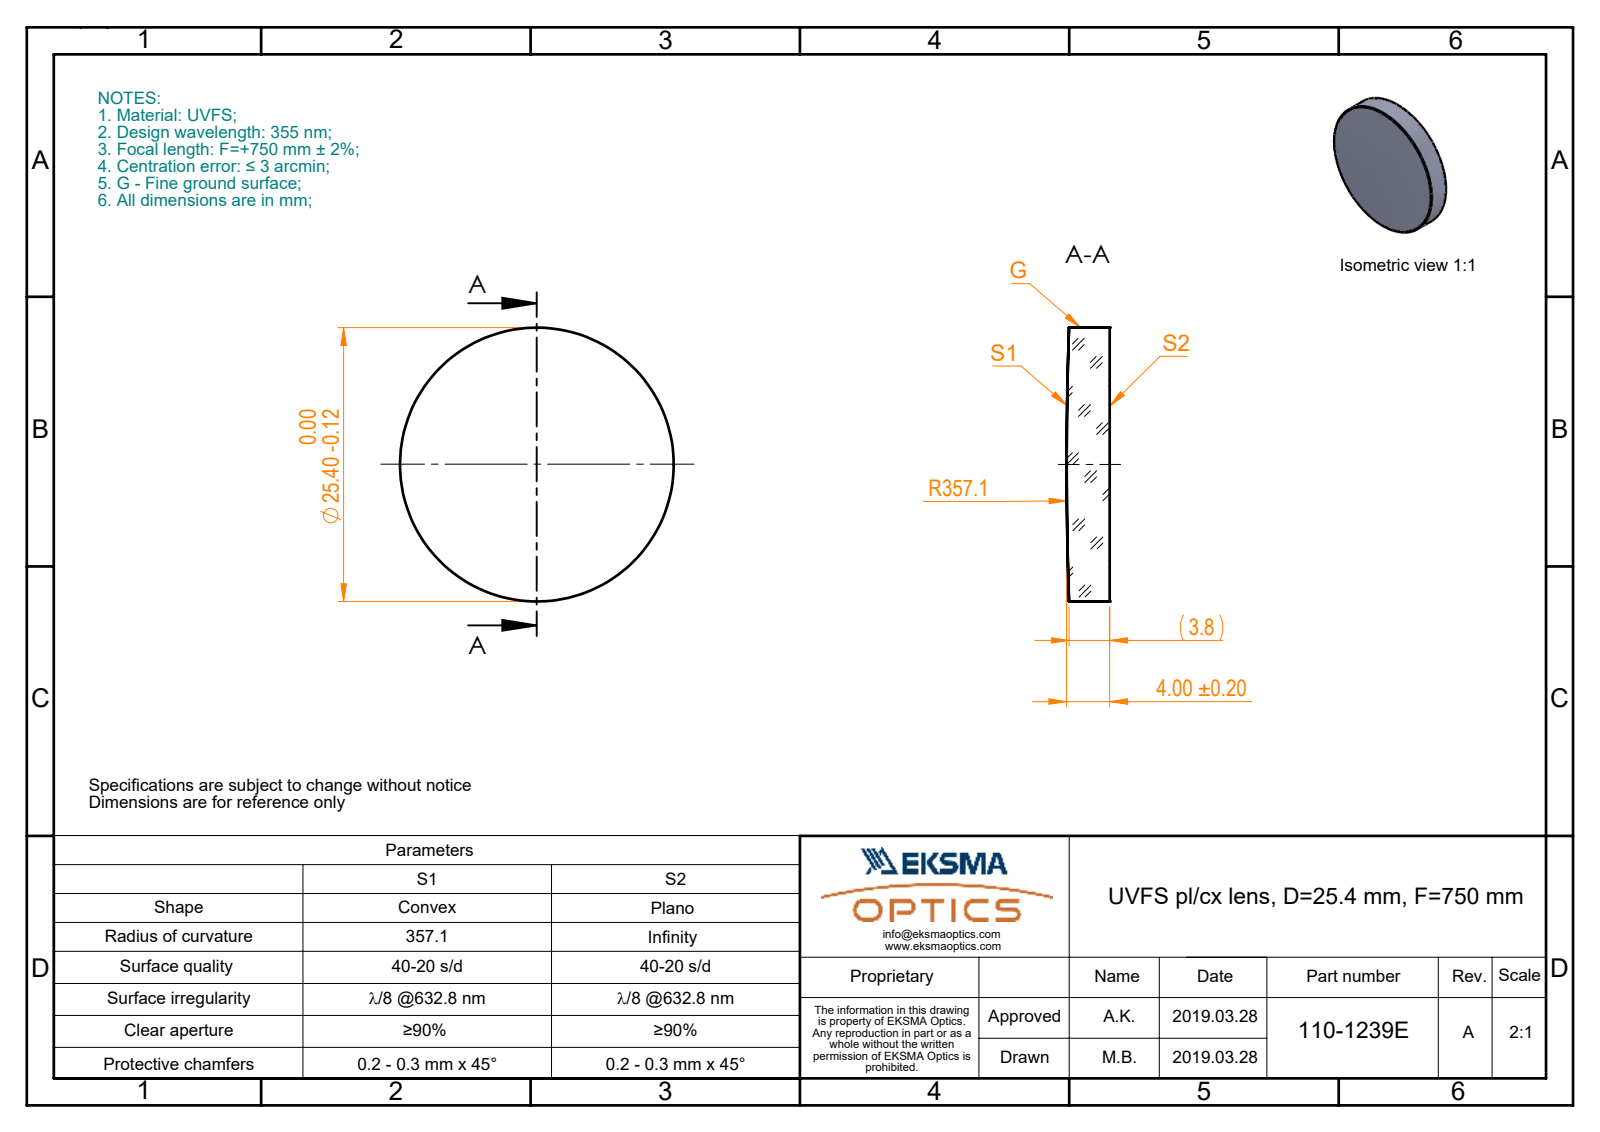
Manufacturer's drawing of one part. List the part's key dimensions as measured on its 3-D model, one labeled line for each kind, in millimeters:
Part name (STEP PRODUCT): 110-1239E UVFS pl-cx 25.4 F750
STEP written by: SolidWorks 2017 (CONFIG_CONTROL_DESIGN)
Units: millimetres
Bodies: 1 solid, 5 faces (1 planar, 2 cylindrical, 2 other)
Overall size (bounding box): 25.4 × 25.4 × 4
Volume: 1 970 mm³ · Surface area: 1 315 mm²
Round bosses / shafts (diameter × count): ⌀25.4 ×1
